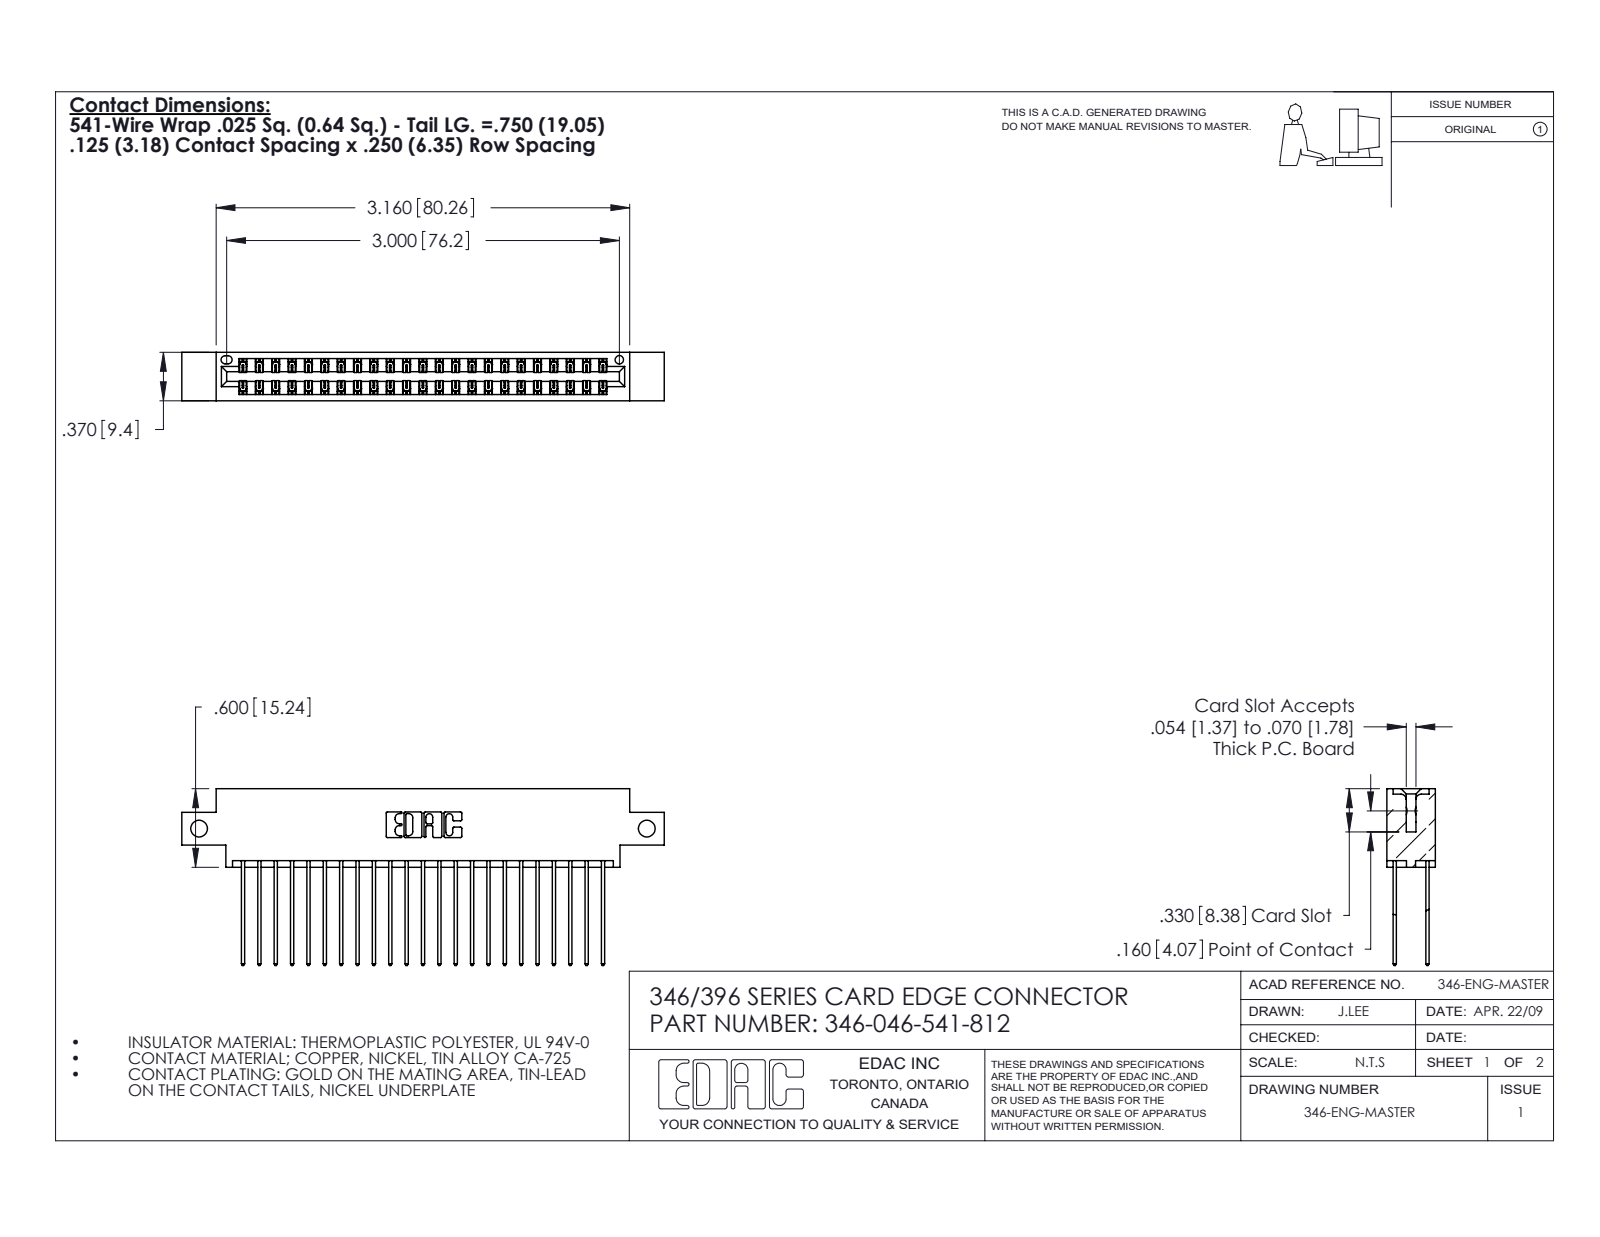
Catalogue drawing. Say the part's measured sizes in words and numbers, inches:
The part is named "345-292-001_345-293-141; 346 Part_0.170 Offset - Side Mount; 346-046-541-812". Its 3-D file was written by "SolidWorks 2020 (CONFIG_CONTROL_DESIGN)". It is 47 solids with 2518 faces: 1690 planar, 828 cylindrical and 0 other. Overall it measures 3.685 by 1.35 by 0.37 inches. Its volume is 0.549 cubic inches and its surface area 20.74 square inches. Round holes: 2 of diameter 0.128, 1 of diameter 0.064. Partial cylindrical surfaces (rounded edges, fillets, slot ends): 69 of radius 0.006, 46 of radius 0.01, 22 of radius 0.01, 6 of radius 0.007, 6 of radius 0.031, 3 of radius 0.026, 2 of radius 0.014, 2 of radius 0.022. The main face-to-face distances are 0.048, 0.322, 0.25, 0.072, 0.298, 0.025, 0.37, 0.275, 0.225, 0.148. The hole center spacings are 3.42.
